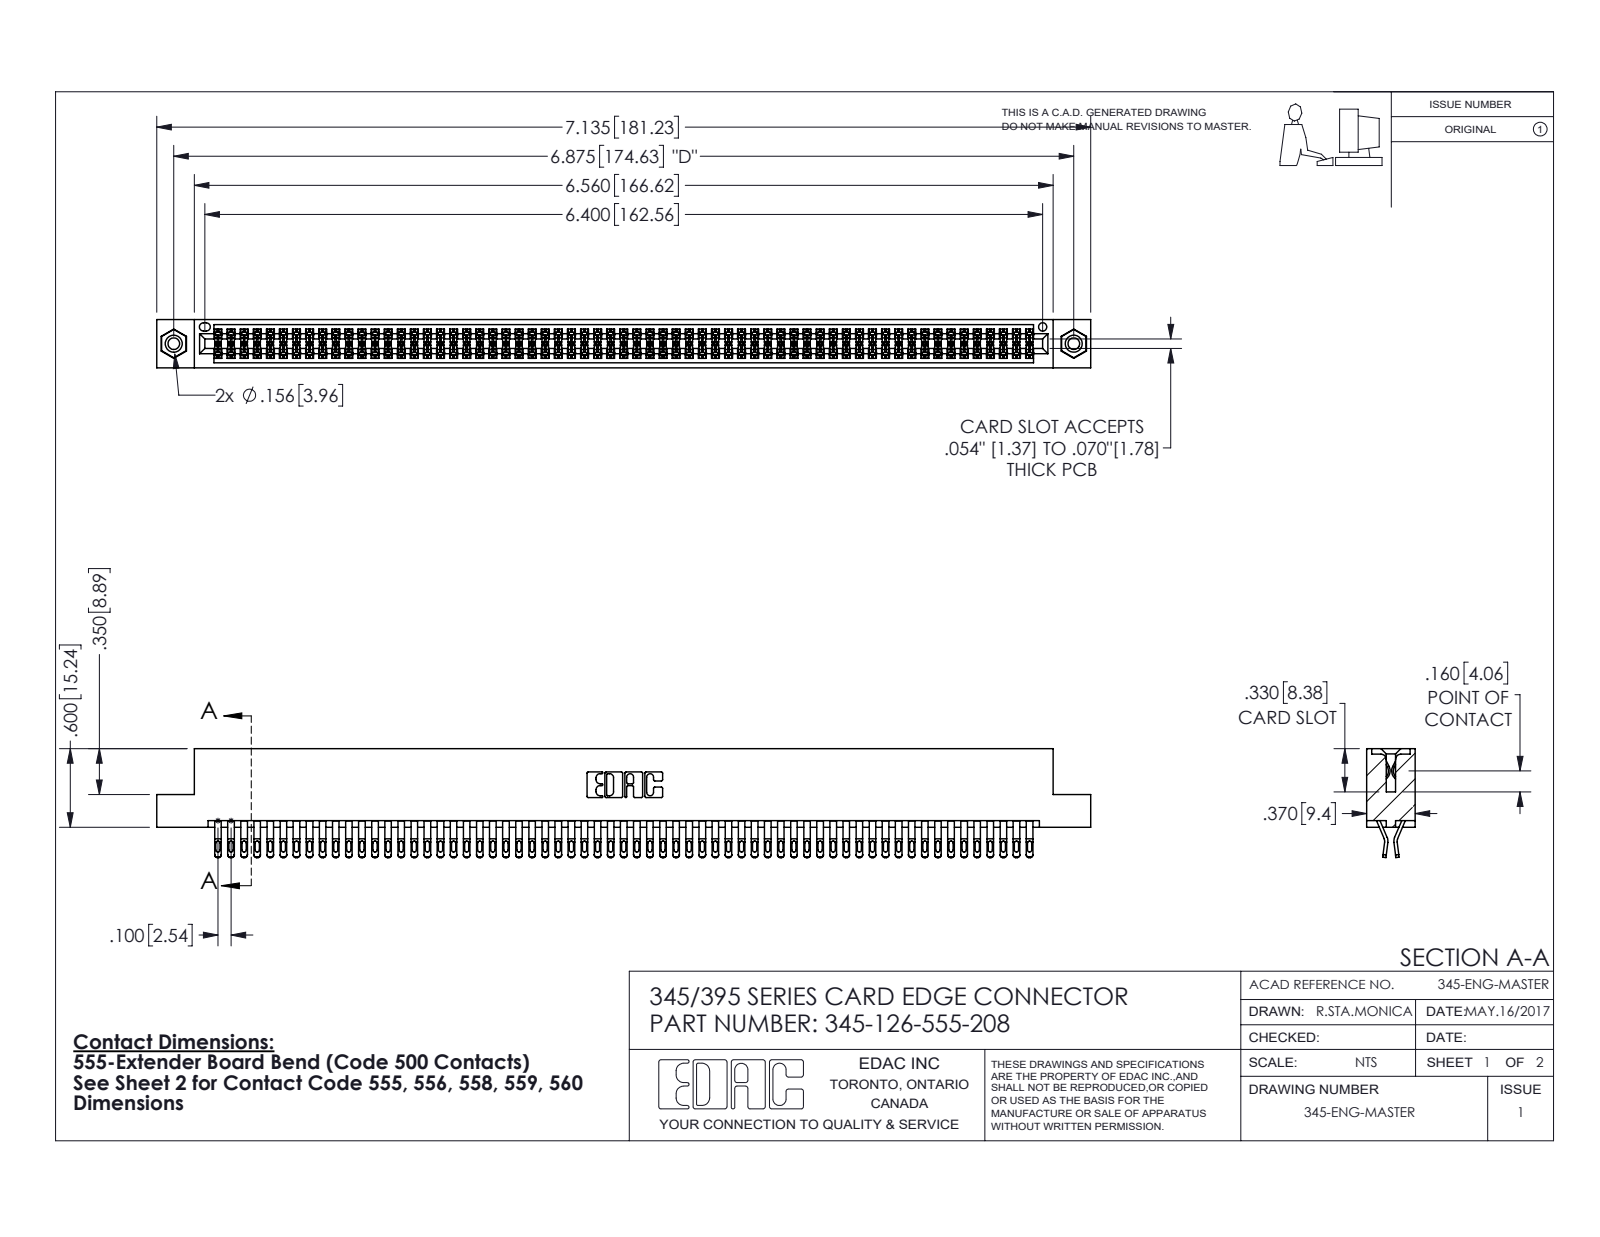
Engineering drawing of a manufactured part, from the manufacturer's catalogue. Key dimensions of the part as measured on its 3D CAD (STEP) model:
Part name (STEP PRODUCT): 345-292-001_555 Tail; 345-126-555-208; 345-250-001_345-250-003-102; 345 Part_Flush Mounting Lugs - 0.156 Dia-TI
STEP written by: SolidWorks 2016 (CONFIG_CONTROL_DESIGN)
Units: inches
Bodies: 129 solids, 7242 faces (4018 planar, 3208 cylindrical, 16 other)
Overall size (bounding box): 7.135 × 0.832 × 0.37
Volume: 1.108 in³ · Surface area: 44.23 in²
Round holes (diameter × count): ⌀0.089 ×2, ⌀0.125 ×2, ⌀0.156 ×2, ⌀0.064 ×1
Round bosses / shafts (diameter × count): ⌀0.155 ×2
Partial cylindrical surfaces — rounded edges, fillets, slot ends (radius × count): R0.016 ×315, R0.02 ×252, R0.006 ×189, R0.01 ×22, R0.007 ×6, R0.031 ×6, R0.026 ×3, R0.01 ×2
Main face-to-face distances: 0.072, 0.298, 0.025, 0.37, 0.2, 0.098, 0.272, 0.225, 0.175, 0.149
Hole centre spacings: 0.27, 6.639, 6.875
